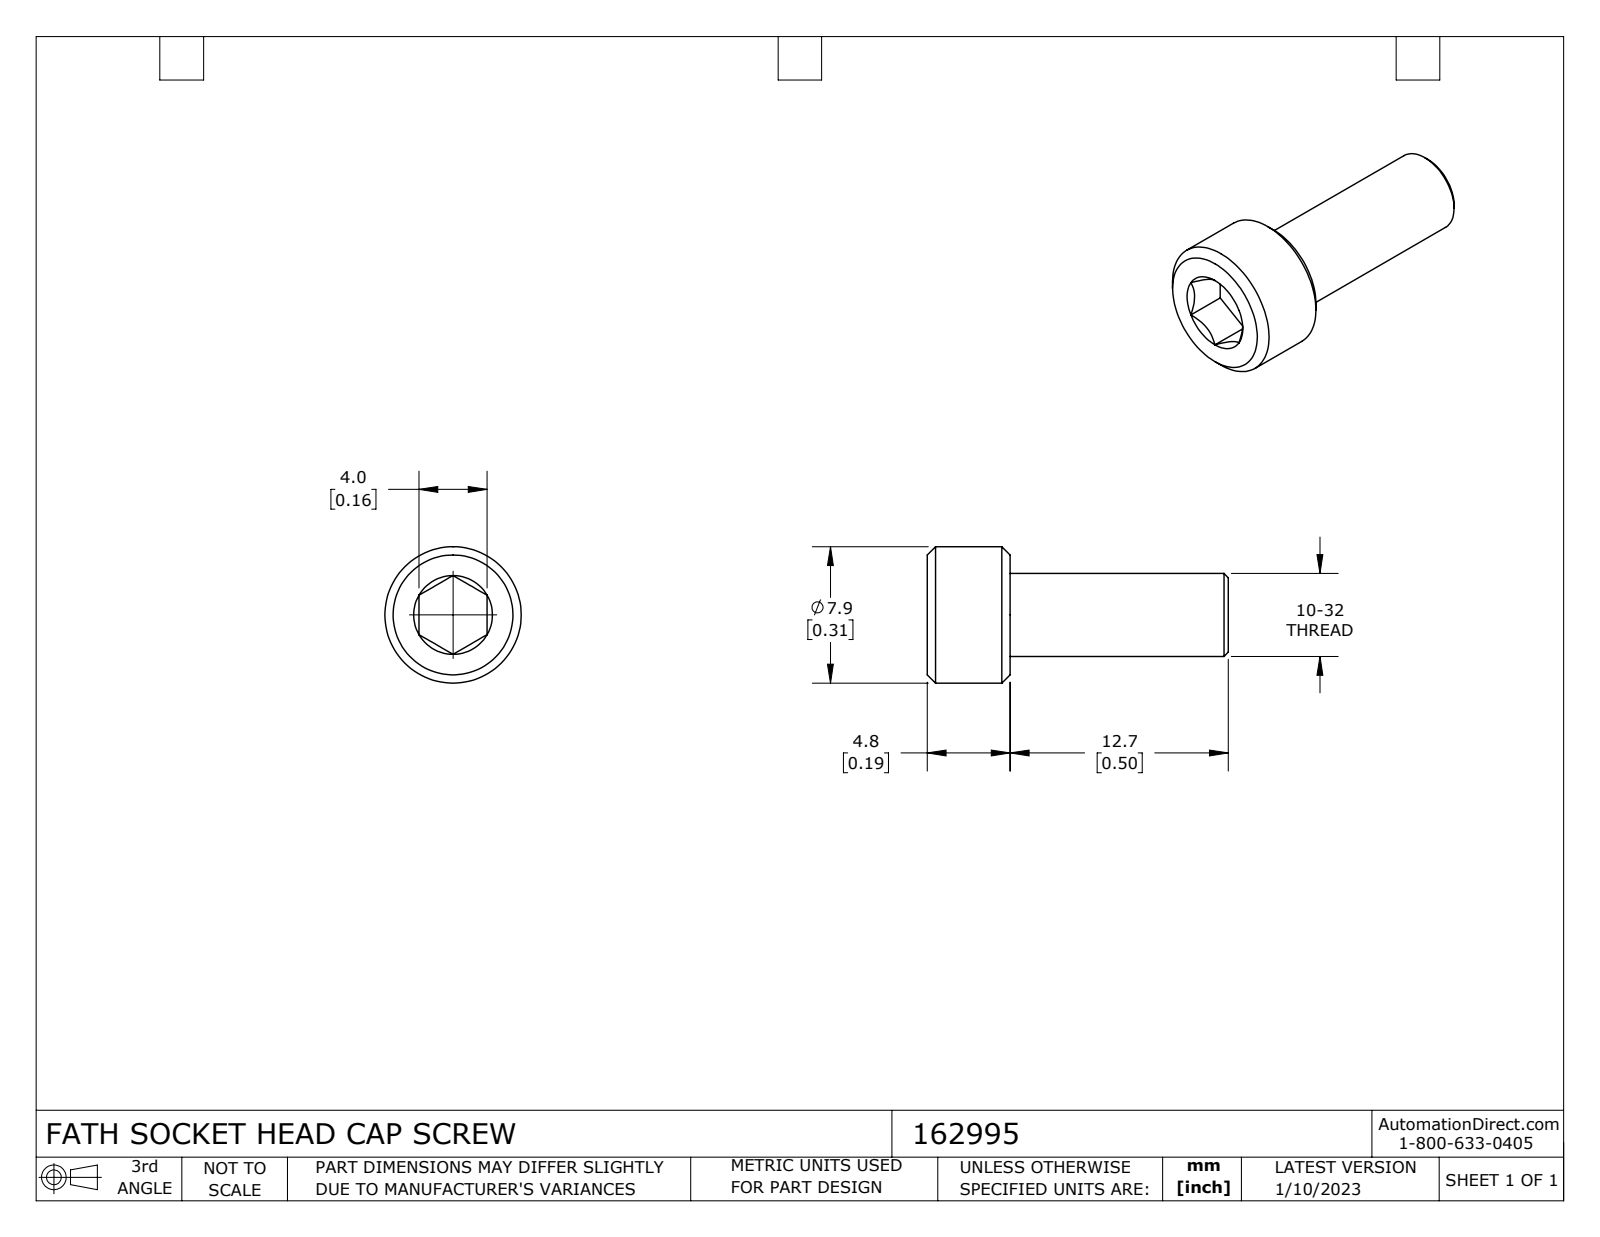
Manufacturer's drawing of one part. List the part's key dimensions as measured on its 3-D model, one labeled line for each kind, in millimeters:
Part name (STEP PRODUCT): 162995
STEP written by: SolidWorks 2021 (CONFIG_CONTROL_DESIGN)
Units: millimetres
Bodies: 1 solid, 27 faces (10 planar, 4 cylindrical, 13 other)
Overall size (bounding box): 17.5 × 8 × 8
Volume: 430 mm³ · Surface area: 426 mm²
Round bosses / shafts (diameter × count): ⌀8 ×1, ⌀4.8 ×1
Main face-to-face distances: 2.4, 4.8, 4, 12.7, 17.5, 15.1
